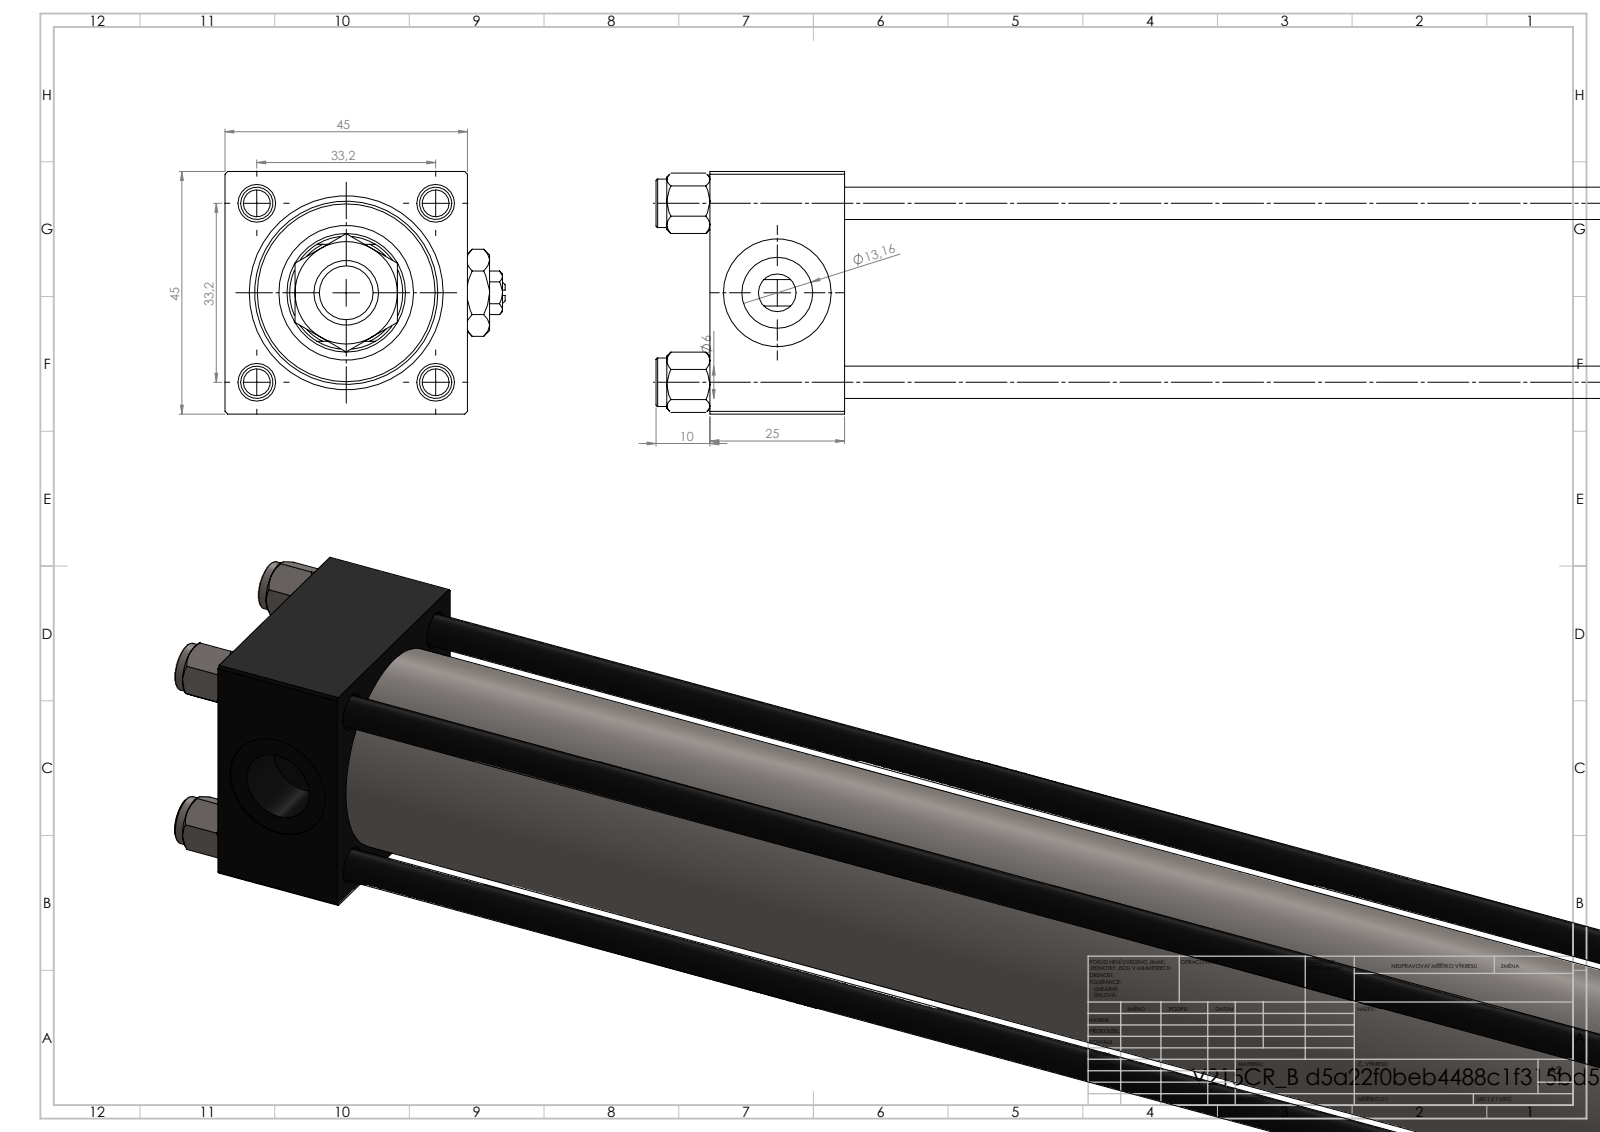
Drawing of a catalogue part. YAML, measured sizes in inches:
part_name: "Zatka_pro_OIL_PORT; V215CR_B_TYCINKA; V215CR_VCP_B; MTA (+3 more)"
step_written_by: "SolidWorks 2019 (CONFIG_CONTROL_DESIGN)"
units: inches
bodies: {solids: 14, faces: 1305, planar: 493, cylindrical: 92, other: 720}
overall_size: [18.543, 2.047, 1.772]
volume: 27.47
surface_area: 283.6
round_holes:
  - {diameter: 0.236, count: 4}
  - {diameter: 0.276, count: 2}
  - {diameter: 0.518, count: 2}
  - {diameter: 0.787, count: 2}
  - {diameter: 0.413, count: 1}
  - {diameter: 0.866, count: 1}
  - {diameter: 0.945, count: 1}
  - {diameter: 0.984, count: 1}
  - {diameter: 1.26, count: 1}
  - {diameter: 1.299, count: 1}
round_bosses_or_shafts:
  - {diameter: 0.354, count: 4}
  - {diameter: 1.496, count: 1}
  - {diameter: 1.339, count: 1}
  - {diameter: 0.472, count: 1}
  - {diameter: 0.394, count: 1}
partial_cylinders:
  - {radius: 0.413, count: 1}
face_to_face_distances: [1.772, 0.984, 15.866, 13.976, 12.992, 1.764, 14.882, 1.89, 14.736, 13.752]
hole_center_spacings: [0.924, 1.307, 1.848, 13.996]
